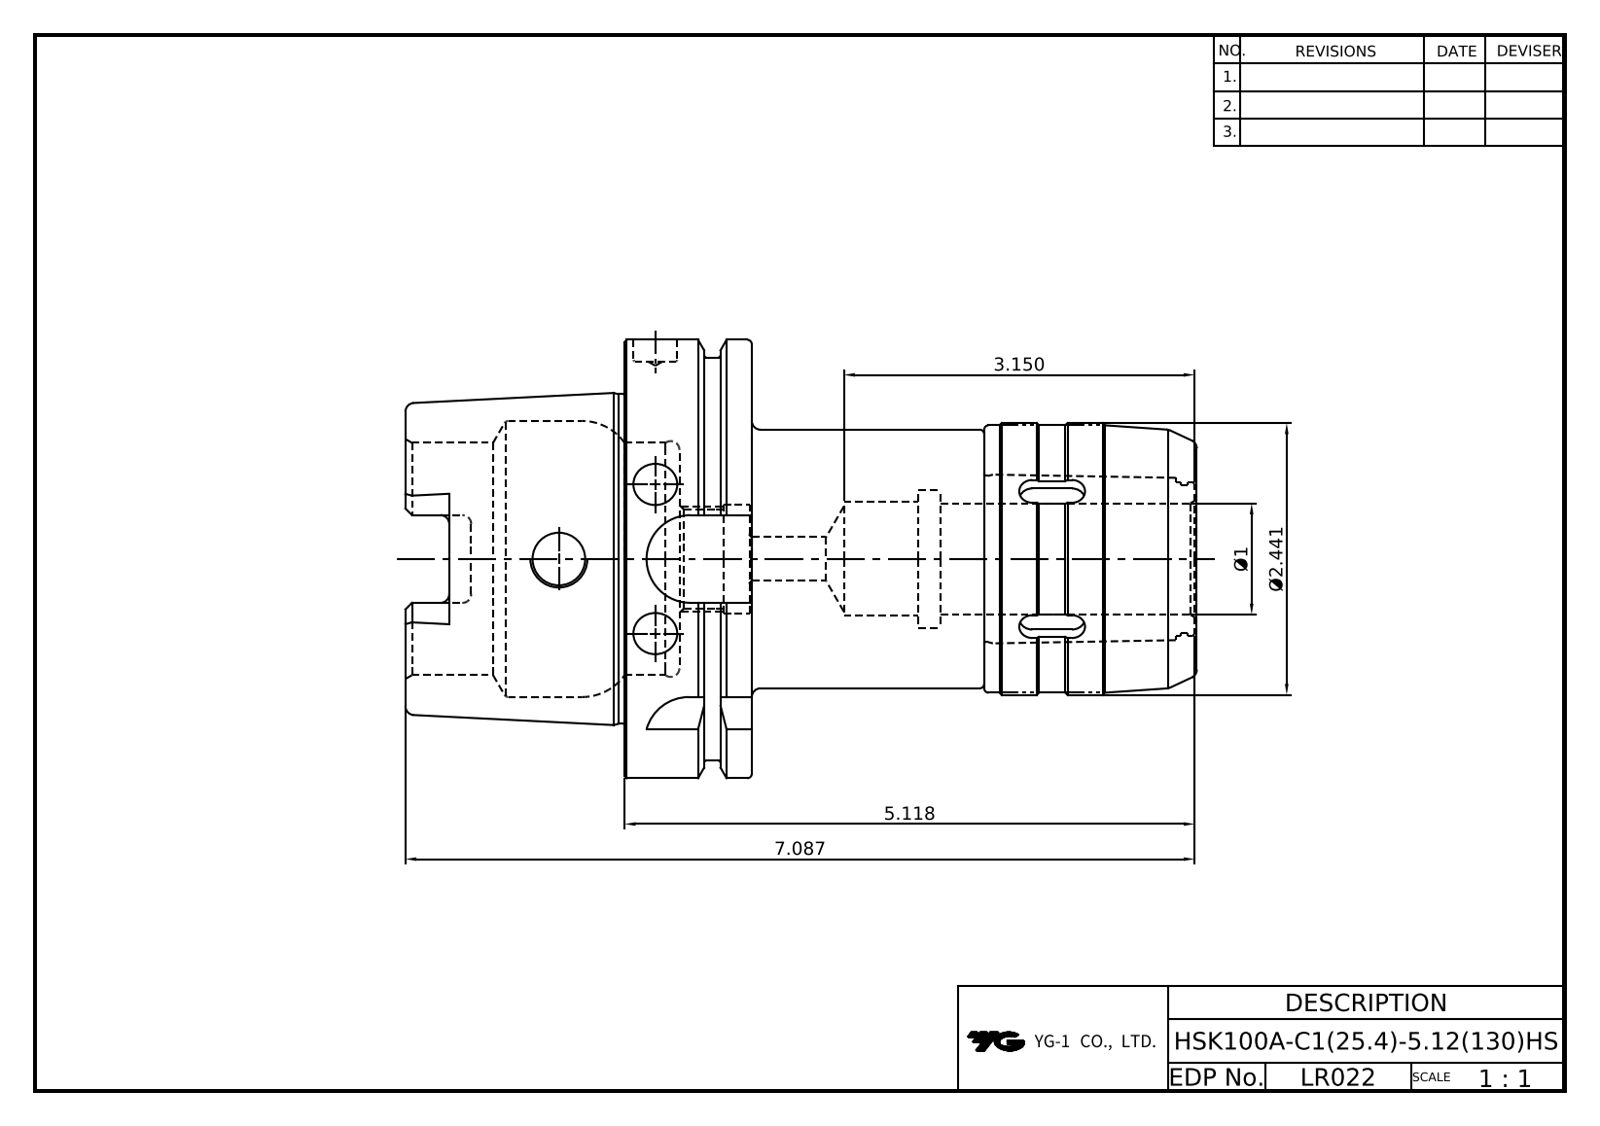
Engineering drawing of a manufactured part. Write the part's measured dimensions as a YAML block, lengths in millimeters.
part_name: "HSK100A-C25.4-130HS; C25-CAP"
step_written_by: "Autodesk Inventor 2020 (AUTOMOTIVE_DESIGN)"
units: millimeters
bodies: {solids: 2, faces: 231, planar: 91, cylindrical: 63, other: 77}
overall_size: [180.5, 100, 100]
volume: 479045
surface_area: 91731
round_holes:
  - {diameter: 10, count: 2}
  - {diameter: 12, count: 2}
  - {diameter: 22.38, count: 1}
  - {diameter: 25, count: 1}
  - {diameter: 25.4, count: 1}
  - {diameter: 26, count: 1}
  - {diameter: 31.6, count: 1}
  - {diameter: 44.5, count: 1}
  - {diameter: 46.45, count: 1}
  - {diameter: 53, count: 1}
  - {diameter: 63, count: 1}
round_bosses_or_shafts:
  - {diameter: 100, count: 1}
  - {diameter: 92, count: 1}
  - {diameter: 75.41, count: 1}
  - {diameter: 62, count: 1}
  - {diameter: 61, count: 1}
  - {diameter: 59, count: 1}
  - {diameter: 35.2, count: 1}
partial_cylinders:
  - {radius: 2, count: 6}
  - {radius: 3, count: 6}
  - {radius: 4.88, count: 4}
  - {radius: 10, count: 4}
face_to_face_distances: [29, 82, 53, 12.5, 16.5, 69.5, 50, 101.5, 62.5, 79]
